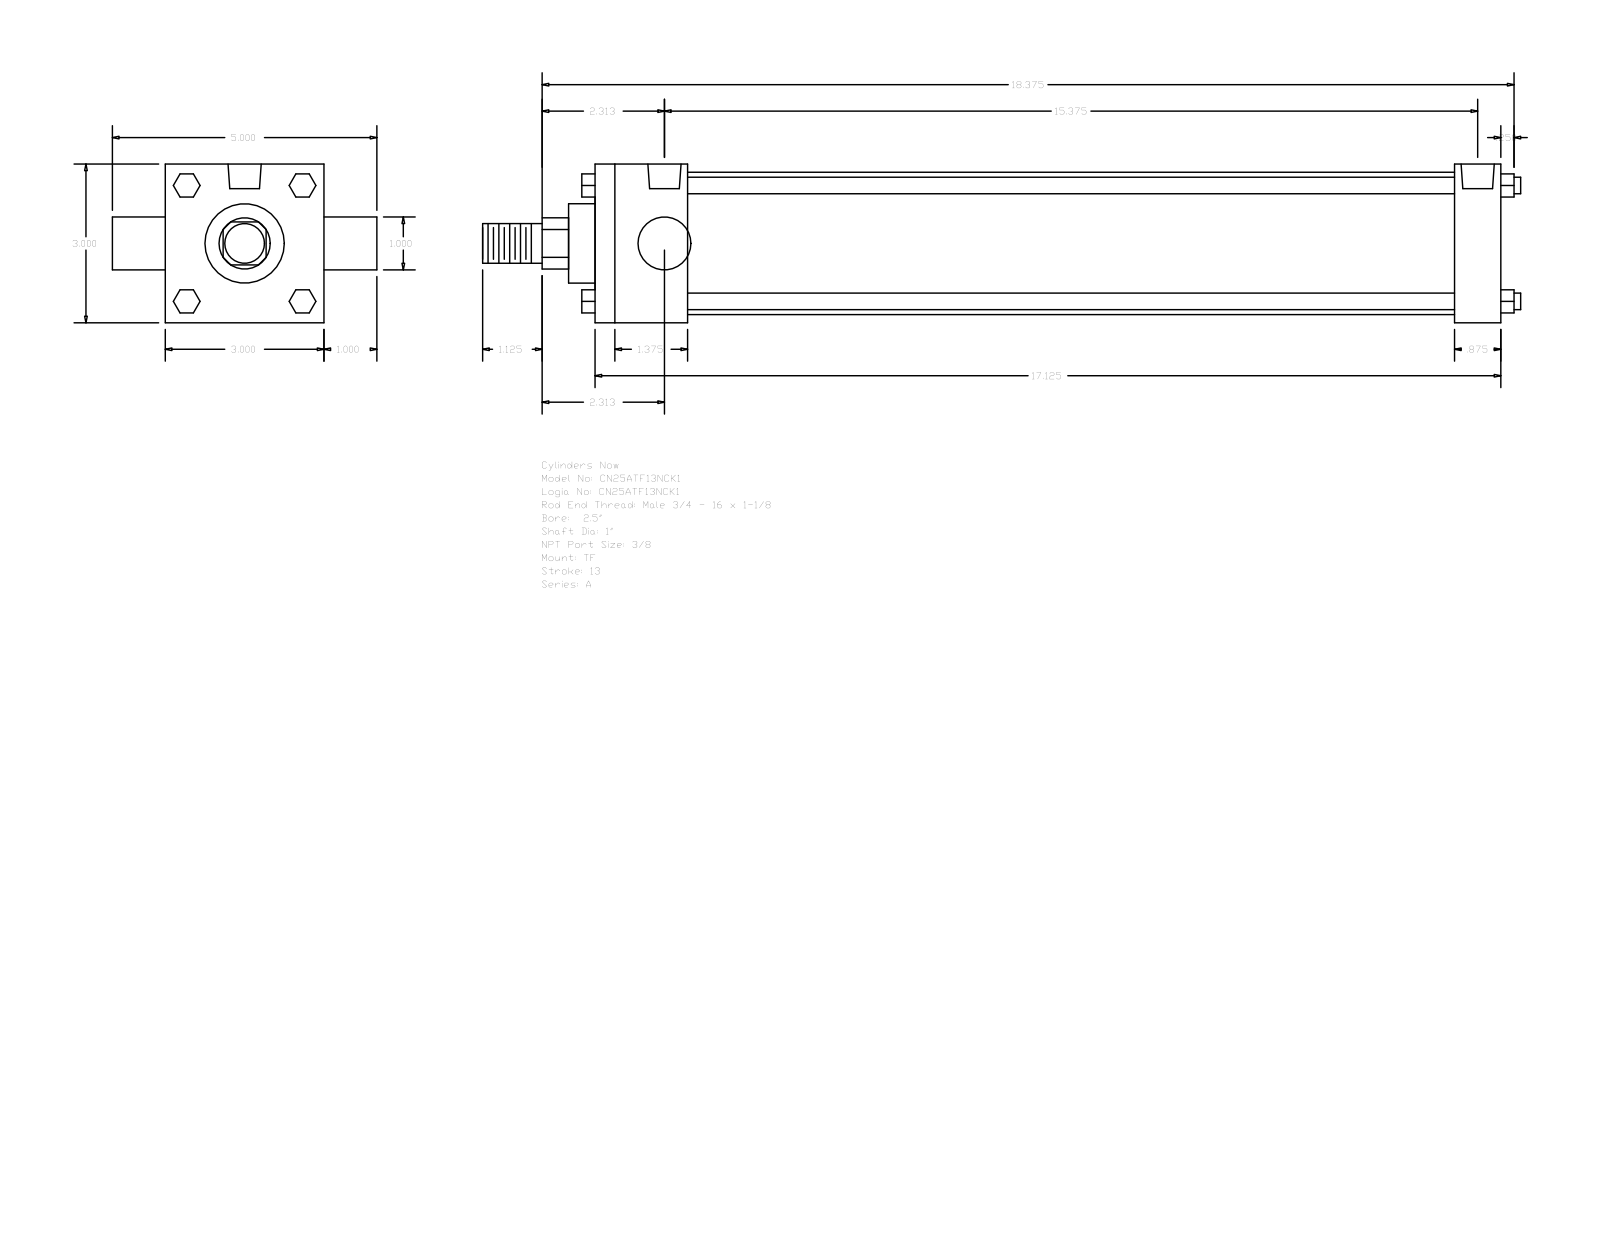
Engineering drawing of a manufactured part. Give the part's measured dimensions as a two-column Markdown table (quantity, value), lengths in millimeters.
| quantity | value |
| --- | --- |
| part name | A_TF__0250_1 |
| STEP written by | GSSL Pune (CONFIG_CONTROL_DESIGN) |
| units | millimeters |
| bodies | 0 solids, 120 faces (92 planar, 28 cylindrical, 0 other) |
| overall size | 498.48 × 127 × 76.2 |
| round holes (diameter × count) | 5.56 × 3, 15.93 × 2 |
| round bosses / shafts (diameter × count) | 7.94 × 4, 25.4 × 2, 68.33 × 1, 38.1 × 1, 19.05 × 1 |
| partial cylindrical surfaces (radius × count) | 12.29 × 1 |
| main face-to-face distances | 76.2, 434.98, 44.45, 412.75, 368.3, 390.53, 22.23, 25.4, 101.6, 447.68 |
| hole center spacings | 2.38, 392.9, 390.52, 395.28 |
